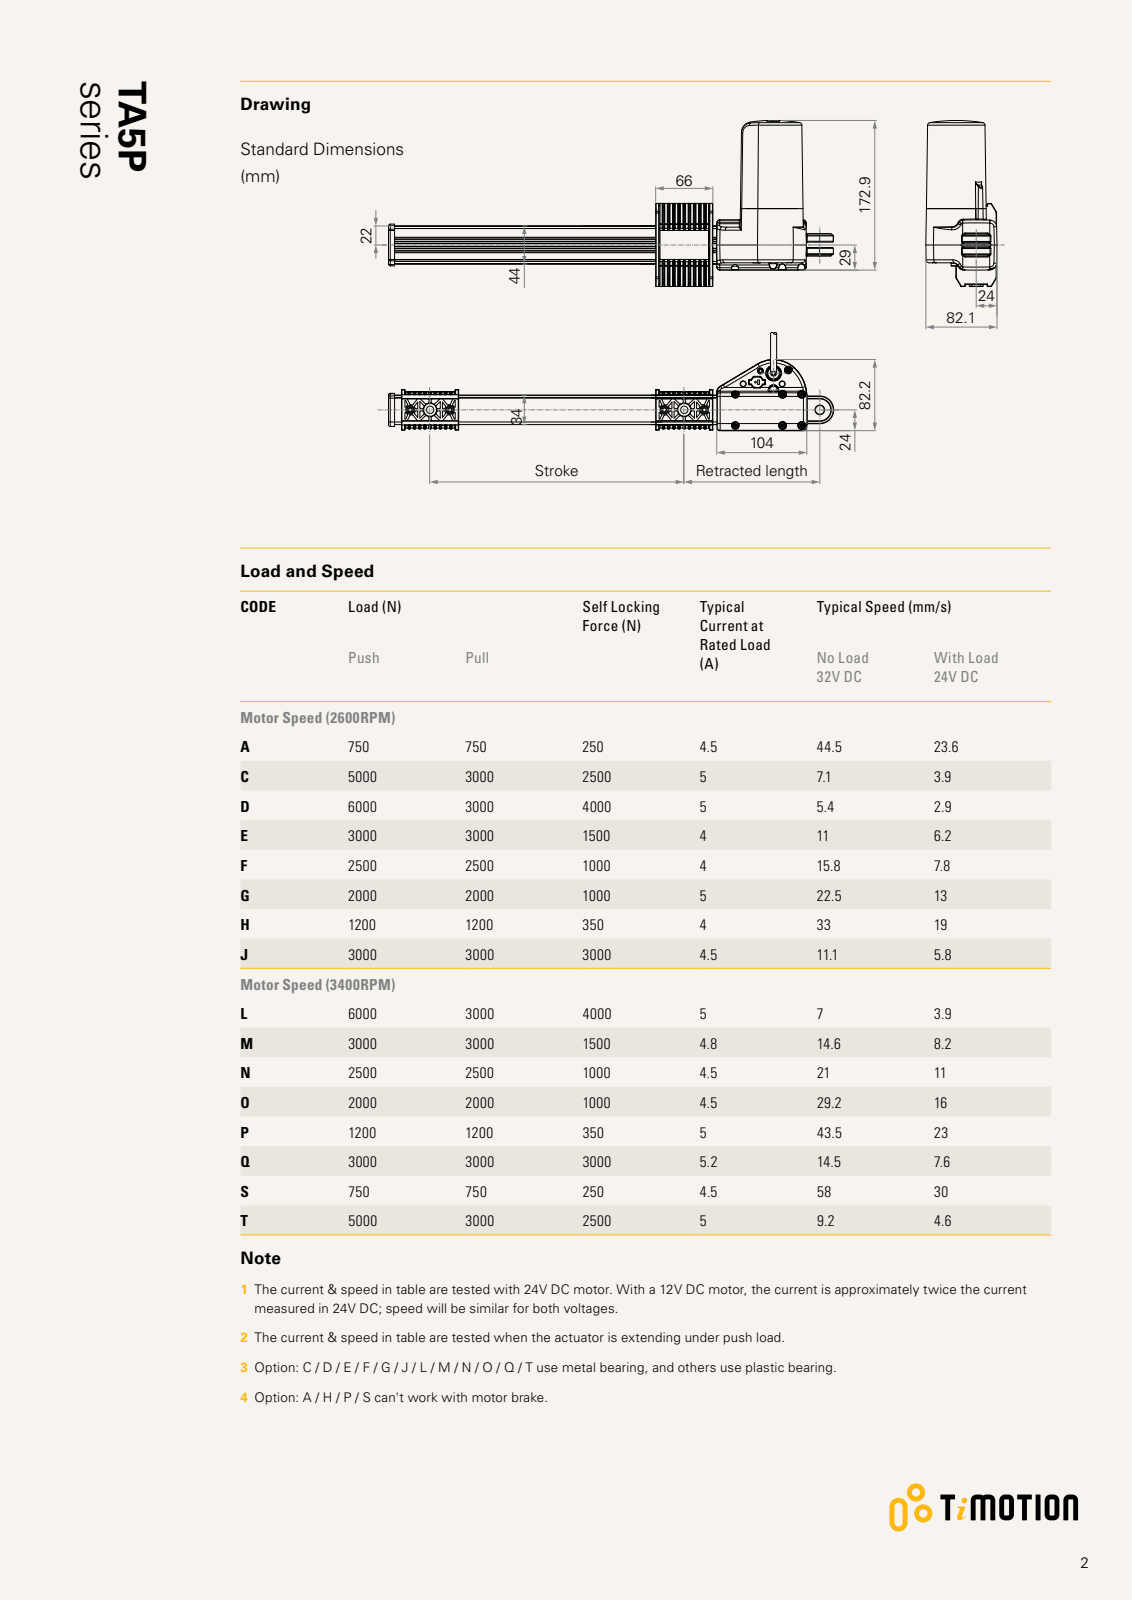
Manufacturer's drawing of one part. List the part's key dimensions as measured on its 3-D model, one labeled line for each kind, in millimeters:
Part name (STEP PRODUCT): TA5P; 外管; 本體; NUT (+1 more)
STEP written by: SolidWorks 2010 (CONFIG_CONTROL_DESIGN)
Units: millimetres
Bodies: 5 solids, 1787 faces (669 planar, 642 cylindrical, 476 other)
Overall size (bounding box): 406.43 × 172.5 × 82.2
Volume: 961 812 mm³ · Surface area: 258 331 mm²
Round holes (diameter × count): ⌀3.2 ×4, ⌀5.2 ×3, ⌀9.5 ×3, ⌀5.3 ×2, ⌀5.5 ×2, ⌀8.5 ×1, ⌀8.8 ×1, ⌀10 ×1, ⌀10.2 ×1, ⌀10.5 ×1, ⌀16 ×1, ⌀17 ×1
Round bosses / shafts (diameter × count): ⌀7 ×4, ⌀10 ×2, ⌀15.9 ×1
Partial cylindrical surfaces — rounded edges, fillets, slot ends (radius × count): R0.5 ×254, R1 ×103, R3 ×24, R0.2 ×16, R4 ×11, R0.3 ×6, R2.5 ×6, R1.15 ×4
Main face-to-face distances: 2, 42, 4, 44, 4.15, 2.15, 32, 34, 30, 40
Hole centre spacings: 17.03, 12, 23, 24.52, 29, 30.81, 42.85, 46.74
